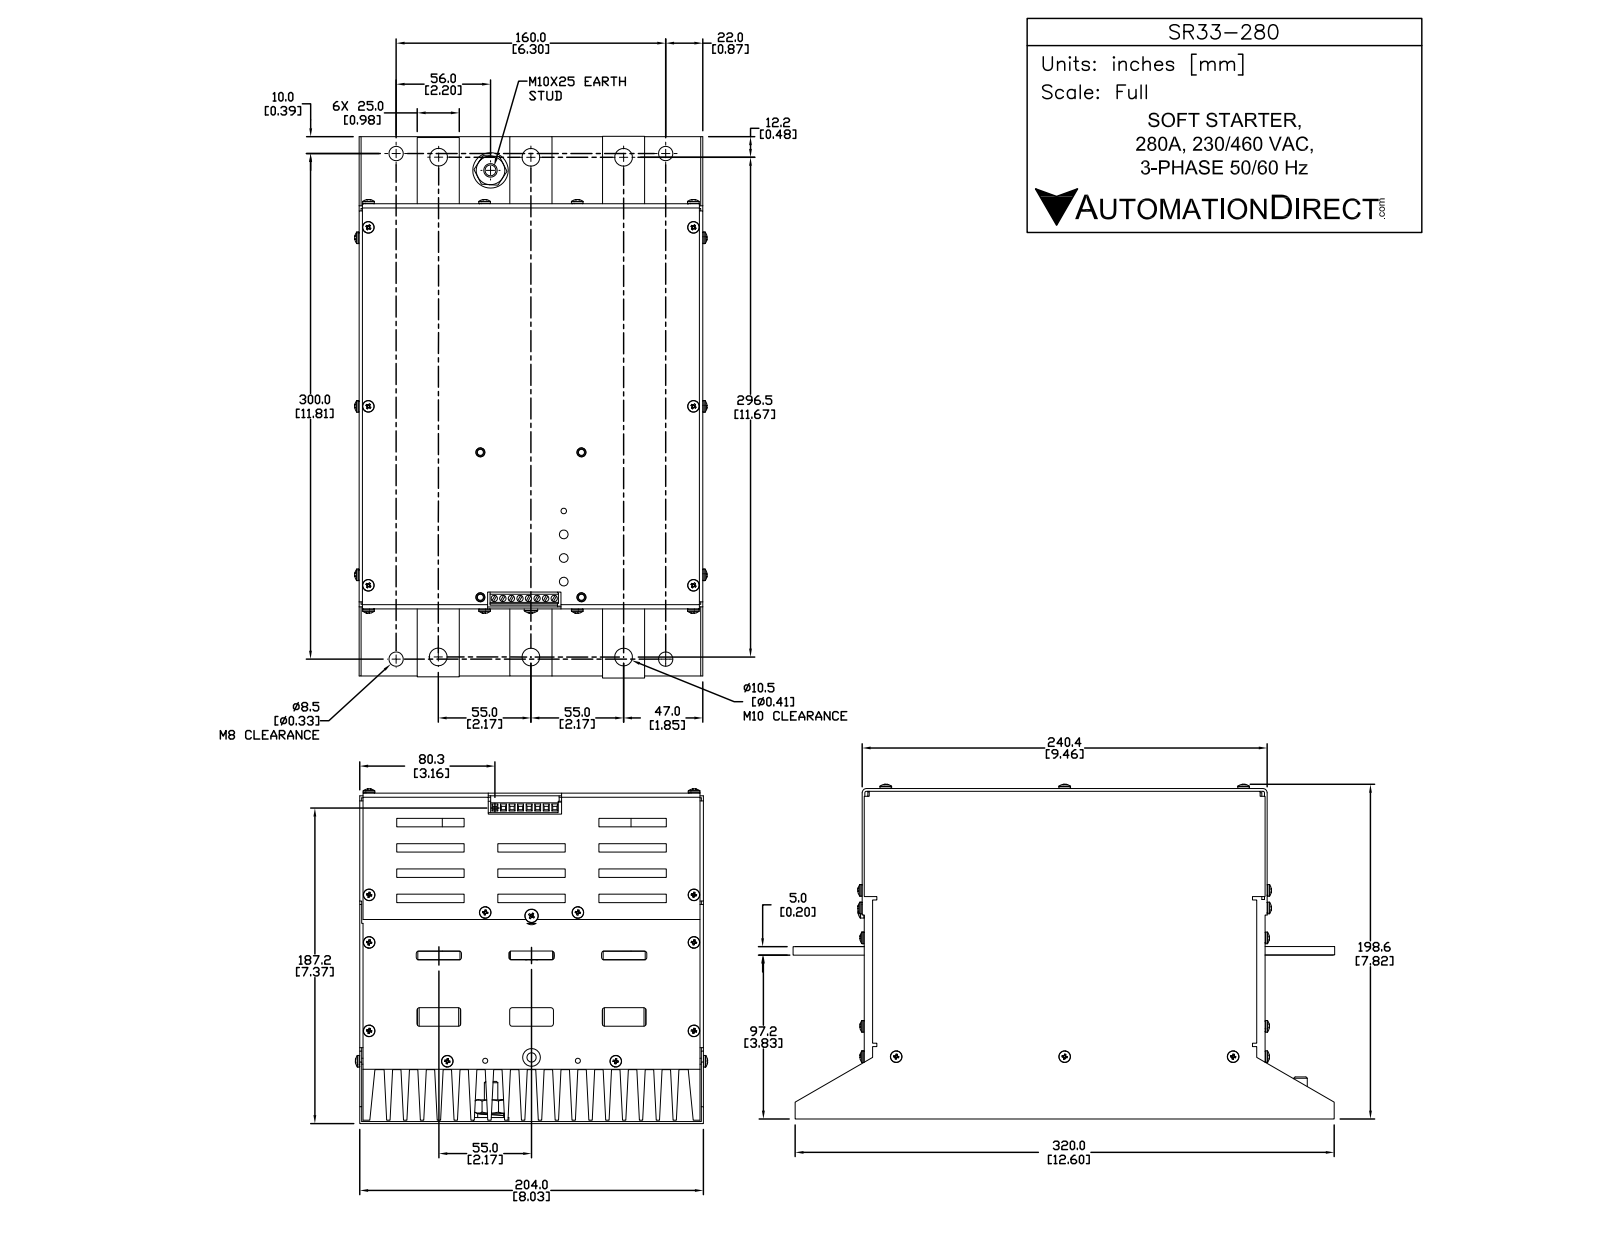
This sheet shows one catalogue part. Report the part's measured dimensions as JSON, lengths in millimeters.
{"part_name": "SR33-280", "step_written_by": "SolidWorks 2013 (AUTOMOTIVE_DESIGN)", "units": "millimeters", "bodies": {"solids": 2, "faces": 1114, "planar": 755, "cylindrical": 153, "other": 206}, "overall_size": [322.8, 203, 199.1], "volume_mm3": 7932000, "surface_area_mm2": 999241, "round_holes": [[3.82, 8], [8.5, 4]], "round_bosses_or_shafts": [[6.9, 14], [16, 7], [8, 7]], "partial_cylinders_radius": [[2, 14], [1, 8]], "face_to_face_distances": [9.99, 19.98, 29.97, 39.96, 49.95, 59.94, 15, 69.93, 79.92, 89.91], "hole_center_spacings": [4.92, 9.84, 14.76, 19.68, 24.6, 29.52, 160, 300]}
